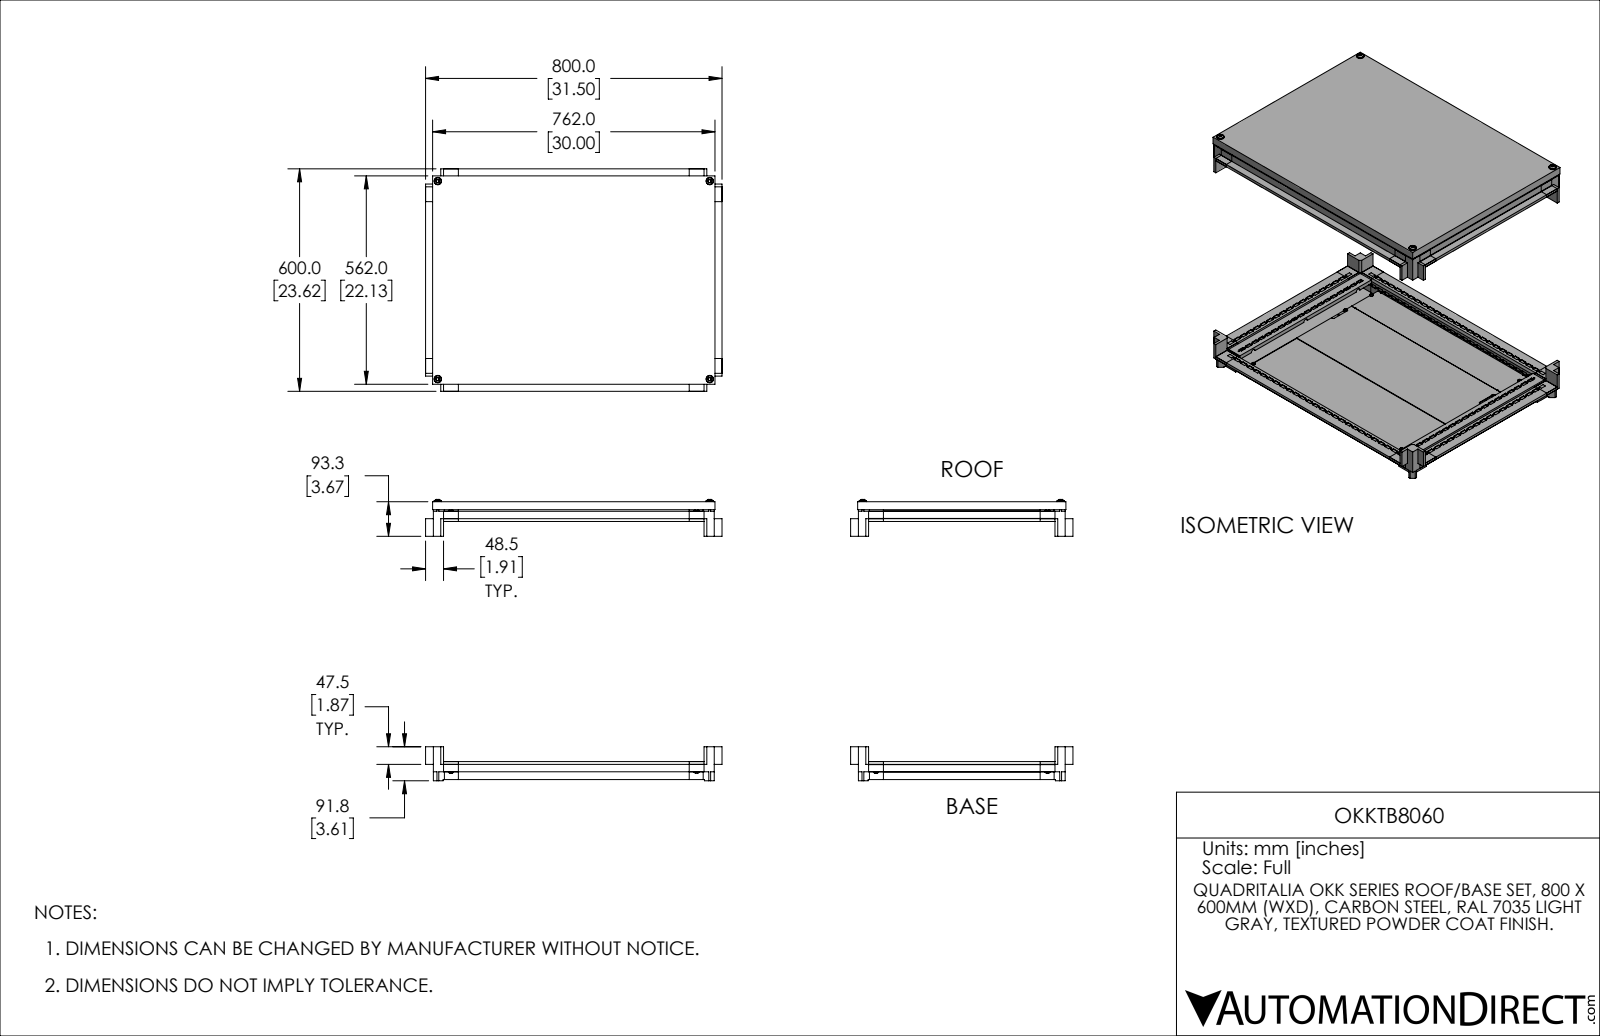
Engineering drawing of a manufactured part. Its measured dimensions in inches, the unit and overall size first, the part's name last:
Units: inches
Overall size (bounding box): 31.496 × 29.875 × 23.622
Round holes (diameter × count): ⌀0.167 ×252, ⌀0.354 ×11, ⌀0.154 ×8, ⌀0.531 ×4, ⌀0.194 ×3, ⌀0.323 ×3
Round bosses / shafts (diameter × count): ⌀0.551 ×11, ⌀0.315 ×11, ⌀0.394 ×9, ⌀0.197 ×6, ⌀0.787 ×4, ⌀0.472 ×4, ⌀0.236 ×4, ⌀0.276 ×1
Partial cylindrical surfaces — rounded edges, fillets, slot ends (radius × count): R0.02 ×264, R0.039 ×24, R0.01 ×16, R0.177 ×12, R0.03 ×9, R0.138 ×8, R0.217 ×6, R0.276 ×3
Main face-to-face distances: 0.059, 28.576, 28.635, 0.787, 1.083, 0.295, 0.098, 1.102, 0.689, 0.807
Hole centre spacings: 0.984, 1.969, 2.953, 3.937, 4.921, 5.906, 6.89, 7.874
Volume: 495.8 in³ · Surface area: 5 058 in²
Bodies: 59 solids, 4631 faces (3546 planar, 926 cylindrical, 159 other)
Part name (STEP PRODUCT): OKKTB8060
STEP written by: SolidWorks 2021 (AUTOMOTIVE_DESIGN)
